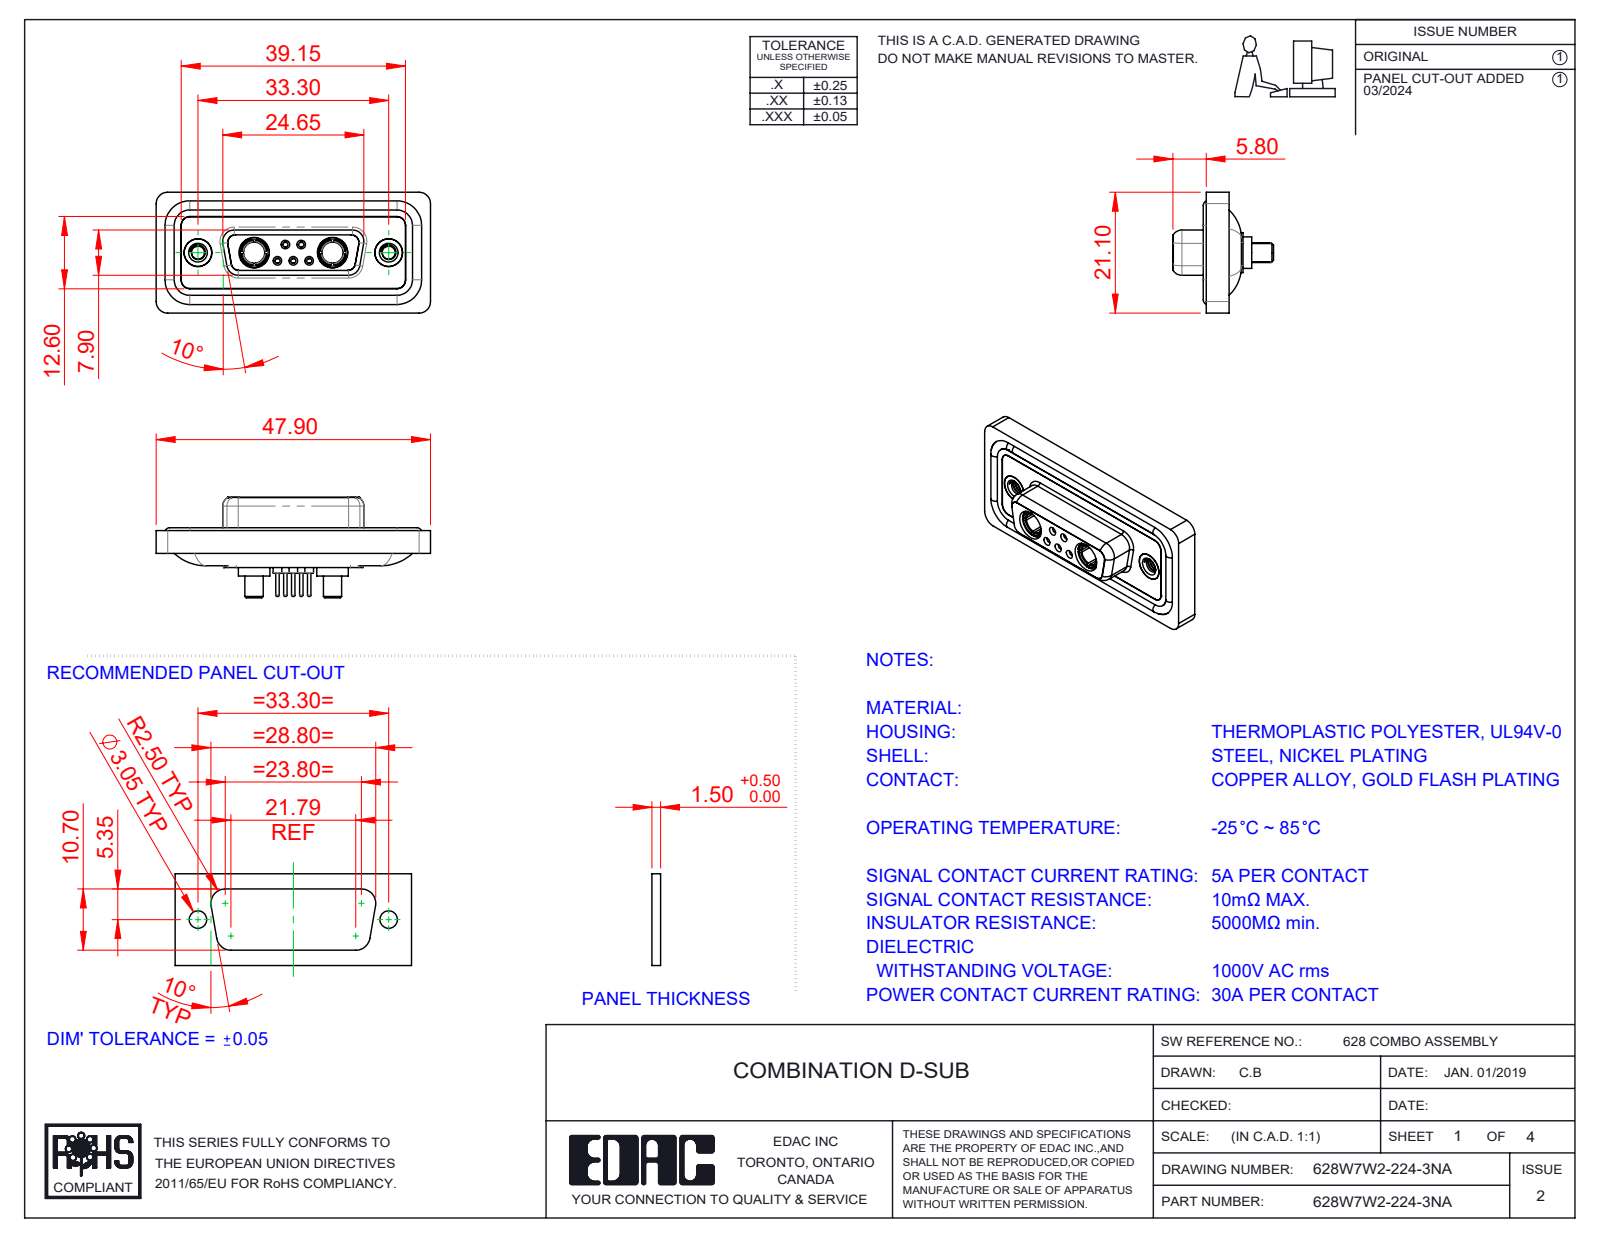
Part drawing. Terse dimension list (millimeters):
name: 628Combo Threaded Rivet_A; 628W7W2-224-3NA; 628Combo Shell Rear_15 Contacts; 628Combo Waterproof Housing_15 Contacts (+5 more)
written by: SolidWorks 2023 (CONFIG_CONTROL_DESIGN)
unit: mm
bodies: 16 solids, 807 faces (238 planar, 331 cylindrical, 238 other)
size: 47.9 × 21.1 × 17.55
volume: 6 093 mm³; area: 9 892 mm²
holes: 5× ⌀0.9, 5× ⌀1.1, 5× ⌀1.5, 5× ⌀2, 4× ⌀4.85, 3× ⌀1.6, 2× ⌀1.7, 2× ⌀2.26, 2× ⌀3.7, 2× ⌀4, 2× ⌀4.05, 2× ⌀5
bosses: 6× ⌀1.6, 5× ⌀2.2, 5× ⌀0.6, 2× ⌀5.5, 2× ⌀5.2, 2× ⌀4.96, 2× ⌀4.95, 2× ⌀4.8
rounds: 22× R1.5, 20× R2, 12× R1.35, 8× R1.6, 4× R0.25, 4× R0.5, 4× R0.6, 4× R0.65
face distances: 0.4, 1.8, 1.6, 0.5, 2.9, 7.45, 1.1, 5.65, 6.6, 7.05
hole spacings: 3.16, 2.77, 9.8, 23.5, 4.31, 4.33, 5.03, 5.04
